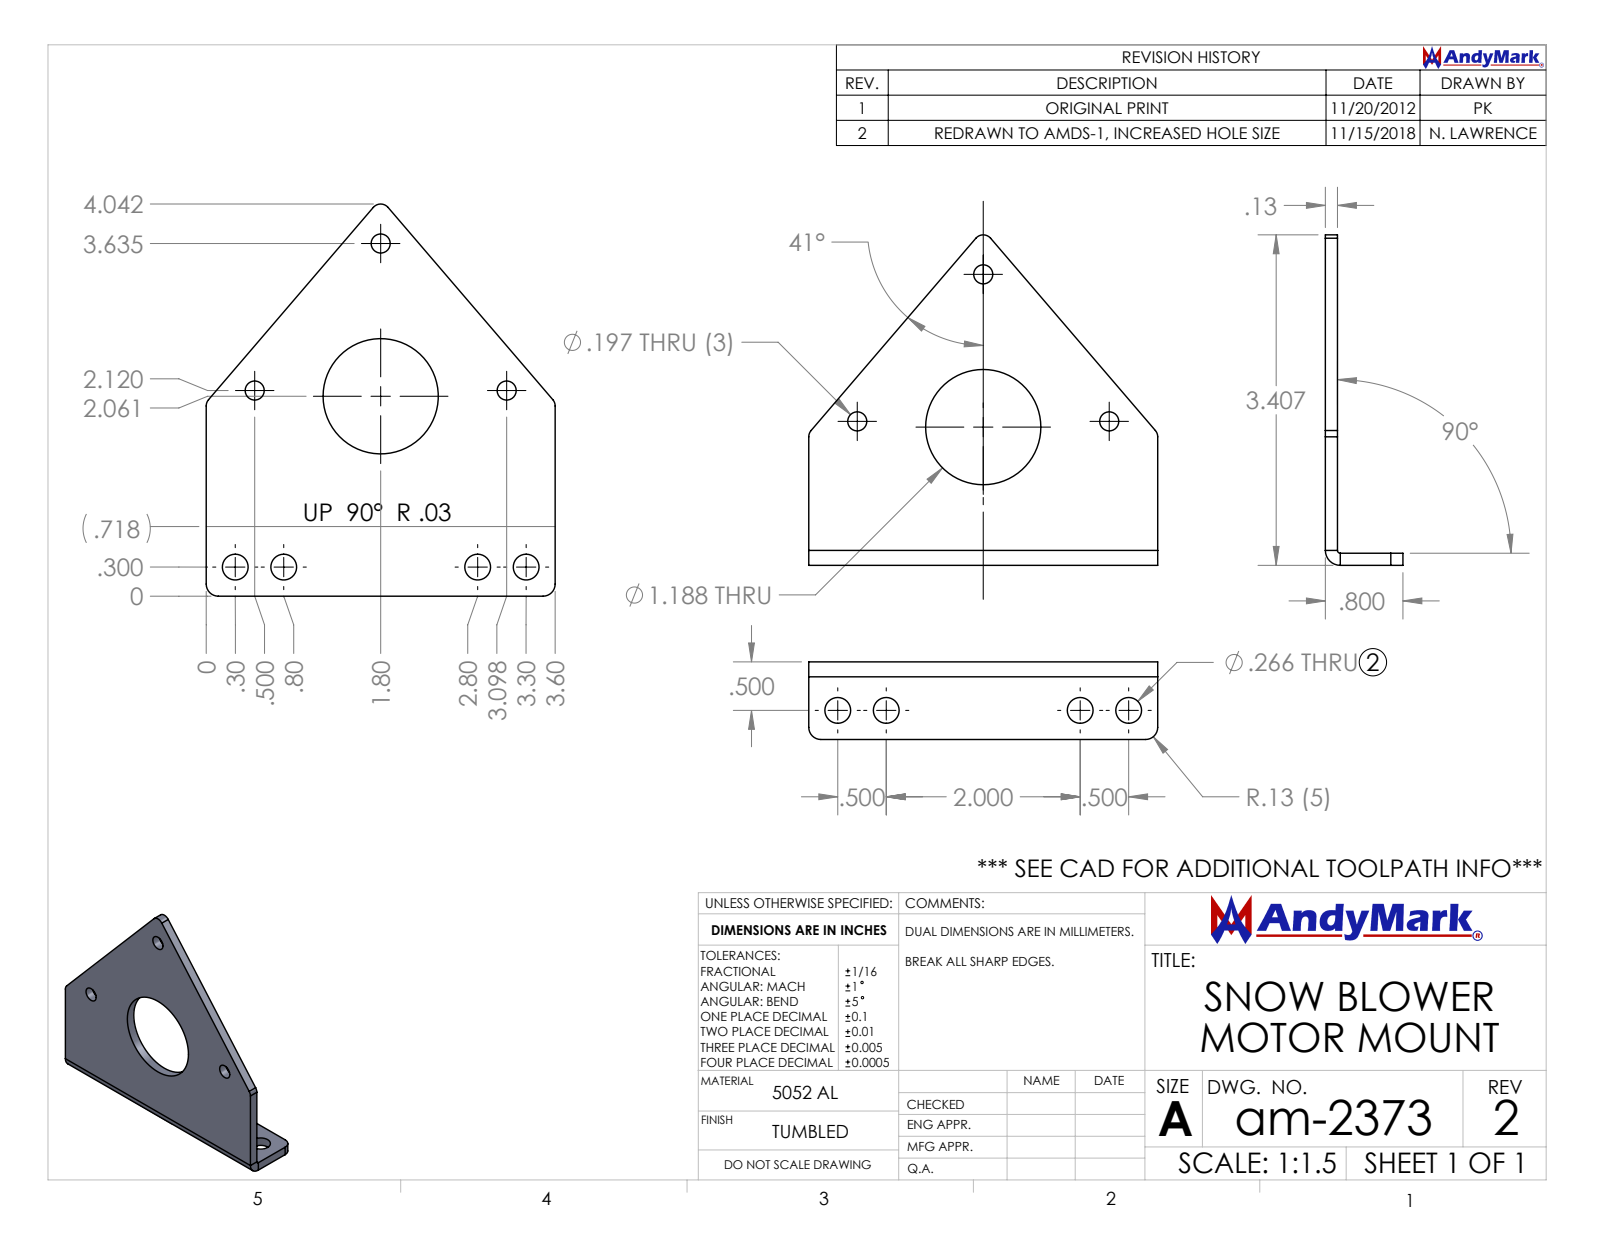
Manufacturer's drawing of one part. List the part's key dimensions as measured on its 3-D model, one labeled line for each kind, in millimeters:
Part name (STEP PRODUCT): am-2373 Snow Blower Motor Mount
STEP written by: SolidWorks 2018 (AUTOMOTIVE_DESIGN)
Units: millimetres
Bodies: 1 solid, 28 faces (13 planar, 15 cylindrical, 0 other)
Overall size (bounding box): 91.4 × 86.5 × 20.3
Volume: 19 520 mm³ · Surface area: 14 060 mm²
Round holes (diameter × count): ⌀6.8 ×4, ⌀5 ×3, ⌀30.2 ×1
Partial cylindrical surfaces — rounded edges, fillets, slot ends (radius × count): R2.5 ×3, R3.2 ×2, R0.7 ×1, R3.9 ×1
Main face-to-face distances: 3.2, 3.2, 17.1, 20.3, 91.4
Hole centre spacings: 12.7, 33, 50.7, 63.5, 40, 50.8, 66, 76.2
